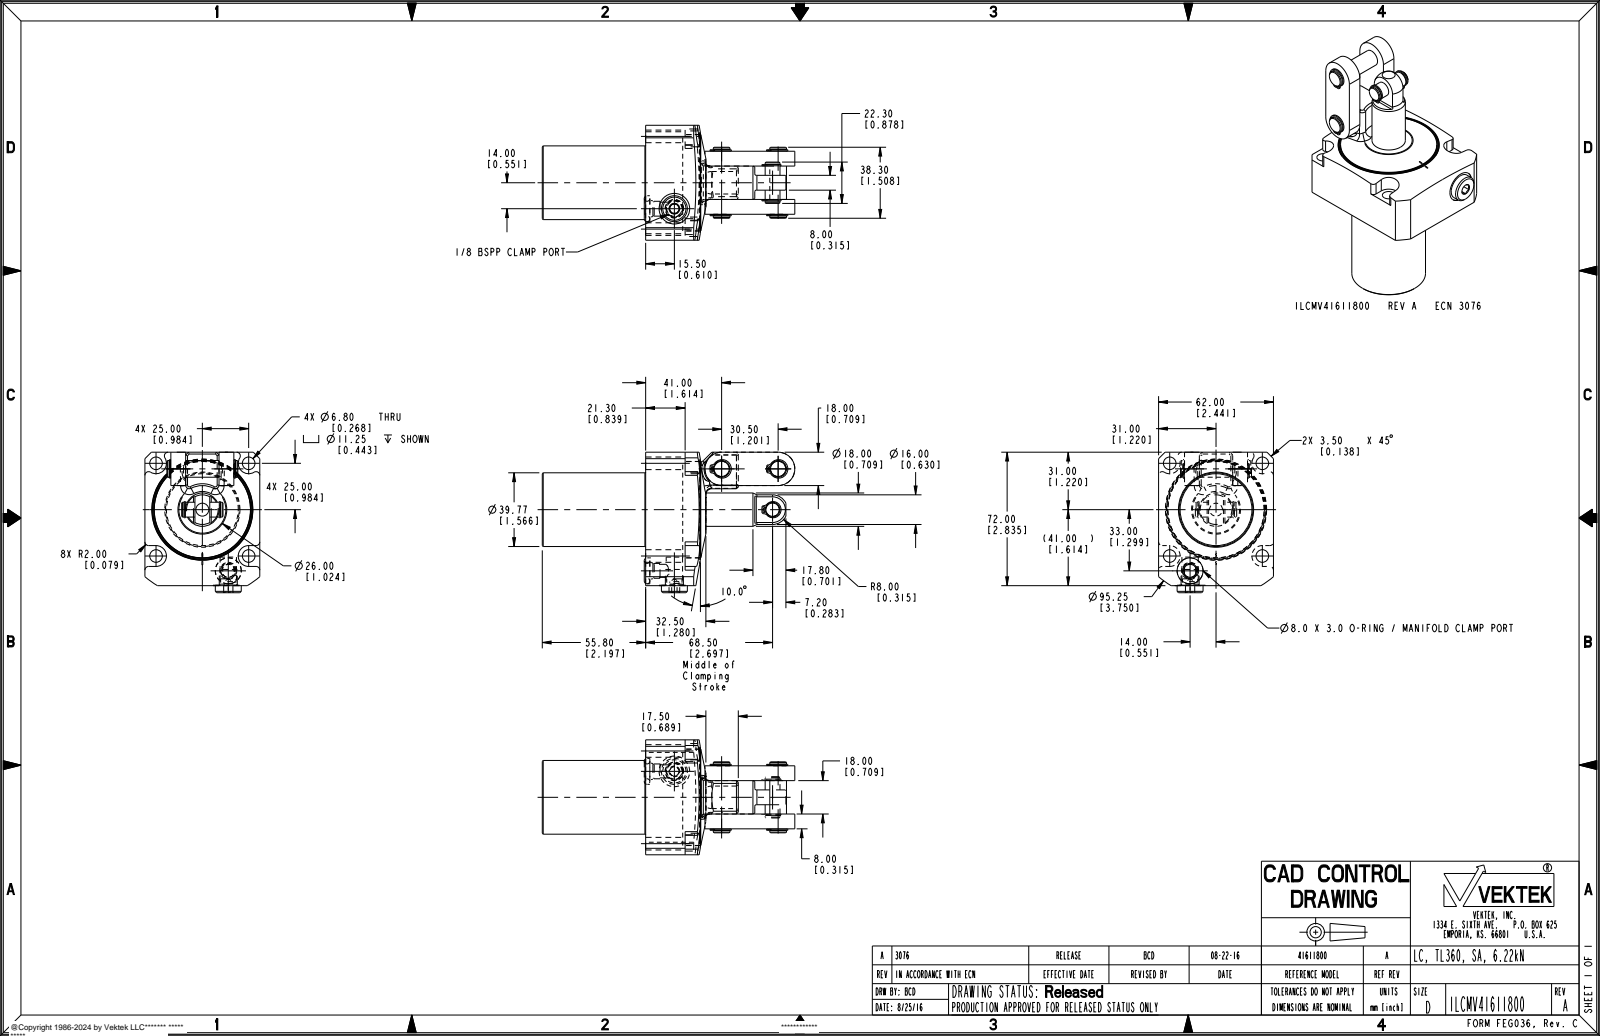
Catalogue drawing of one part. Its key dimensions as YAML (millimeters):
part_name: "ILCMV41611800_BODY; ILCMV41611800_LUG; ILCMV41611800"
step_written_by: "PRO/ENGINEER BY PARAMETRIC TECHNOLOGY CORPORATION, 2013320 (AUTOMOTIVE_DESIGN)"
units: millimeters
bodies: {solids: 3, faces: 345, planar: 120, cylindrical: 155, other: 70}
overall_size: [136.3, 75.81, 62]
volume: 224022
surface_area: 43020
round_holes:
  - {diameter: 1.04, count: 6}
  - {diameter: 6.8, count: 4}
  - {diameter: 5, count: 1}
  - {diameter: 7.04, count: 1}
  - {diameter: 8.84, count: 1}
  - {diameter: 14, count: 1}
  - {diameter: 16.5, count: 1}
  - {diameter: 52.03, count: 1}
round_bosses_or_shafts:
  - {diameter: 9.99, count: 2}
  - {diameter: 9, count: 2}
  - {diameter: 8.38, count: 2}
  - {diameter: 8, count: 2}
  - {diameter: 51.93, count: 1}
  - {diameter: 39.77, count: 1}
  - {diameter: 18, count: 1}
  - {diameter: 14, count: 1}
partial_cylinders:
  - {radius: 2, count: 10}
  - {radius: 1.04, count: 6}
  - {radius: 0.8, count: 4}
  - {radius: 1.76, count: 4}
  - {radius: 5.62, count: 4}
  - {radius: 2.32, count: 2}
  - {radius: 9, count: 2}
  - {radius: 4.38, count: 1}
face_to_face_distances: [20, 62, 14, 48, 8, 55.8, 75.8, 72, 22, 40]
hole_center_spacings: [35.36, 50, 2.34, 22.14, 30.5, 30.59, 35.61, 70.71]
